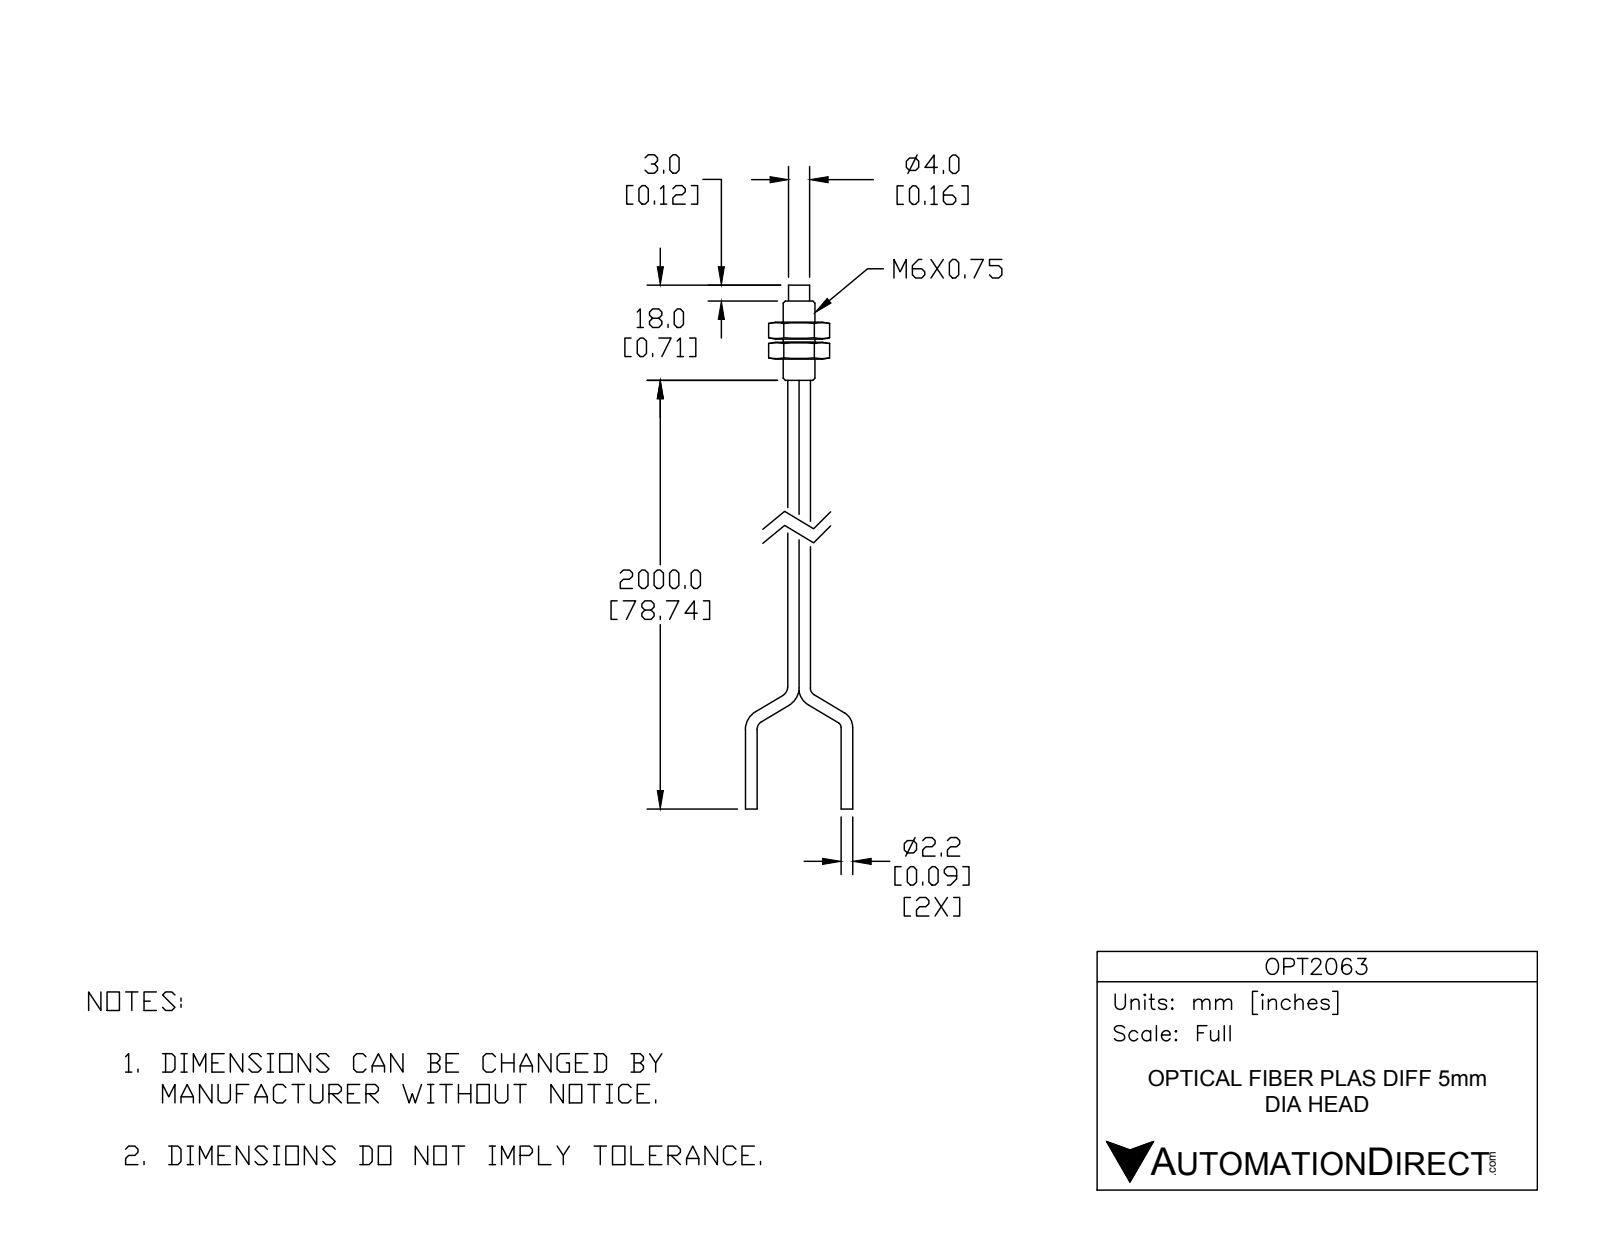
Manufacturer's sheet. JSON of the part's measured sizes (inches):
{"part_name": "OPT2063", "step_written_by": "SolidWorks 2014 (AUTOMOTIVE_DESIGN)", "units": "inches", "bodies": {"solids": 4, "faces": 71, "planar": 27, "cylindrical": 24, "other": 20}, "overall_size": [3.902, 0.799, 0.394], "volume_in3": 0.085, "surface_area_in2": 2.611, "round_bosses_or_shafts": [[0.087, 6], [0.236, 1], [0.157, 1]], "face_to_face_distances": [0.394, 0.126, 0.15, 0.276, 0.024, 0.157, 0.283, 0.307, 0.433, 0.402]}
